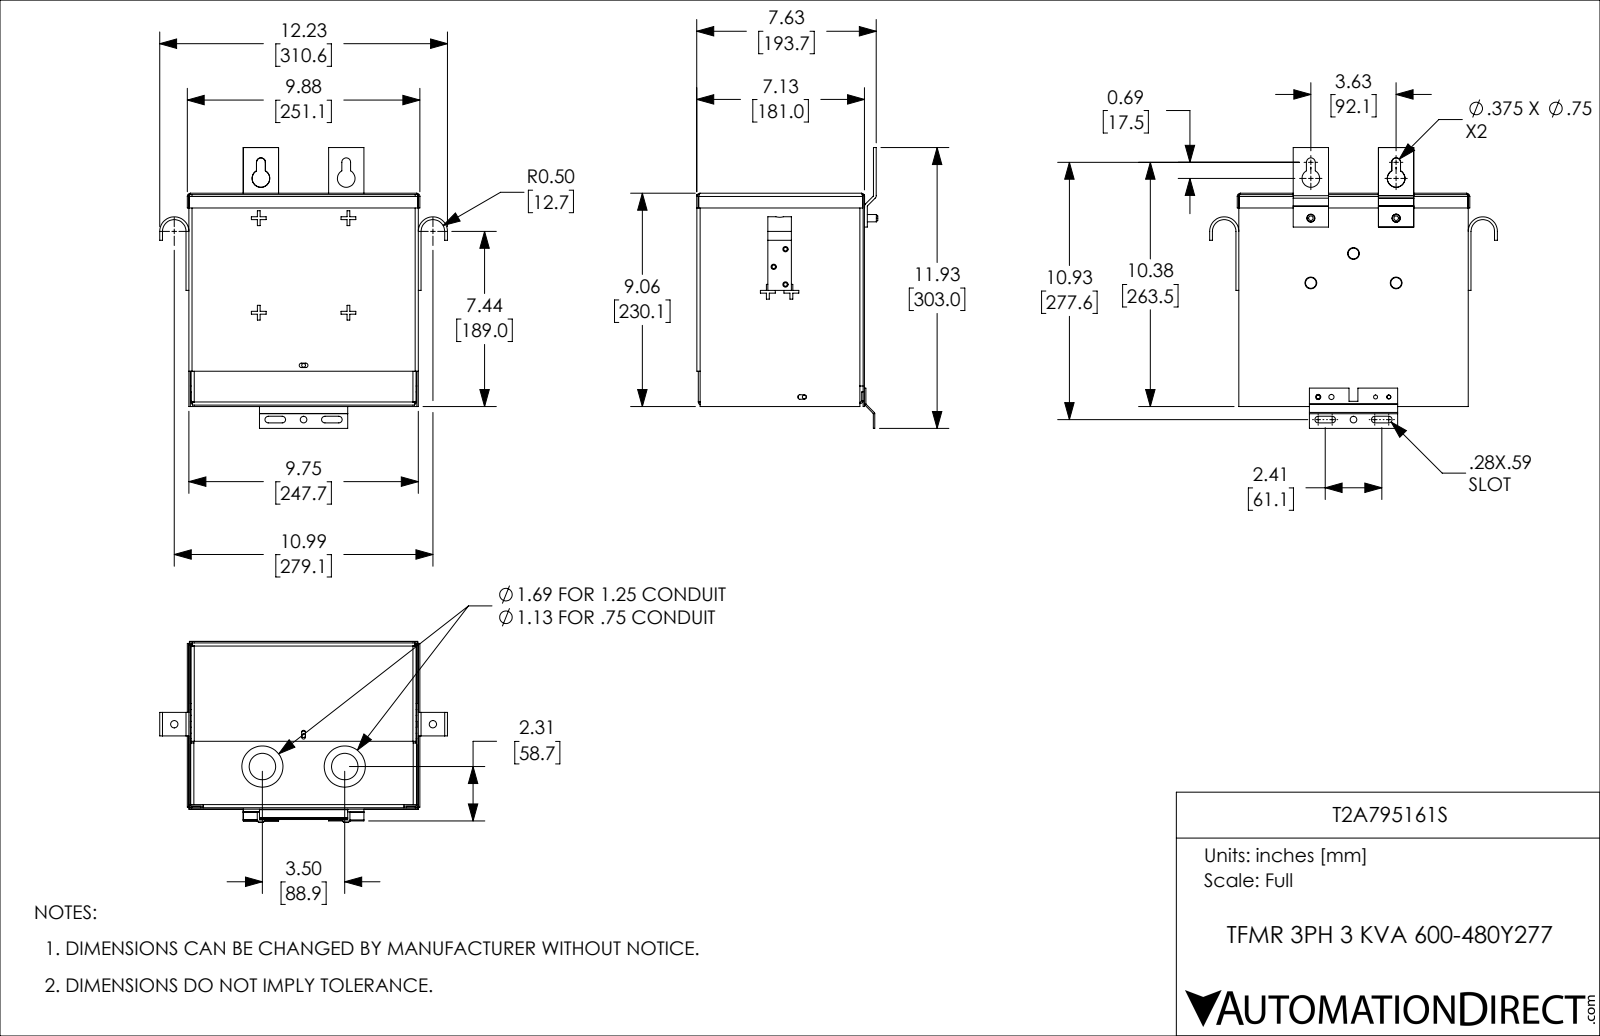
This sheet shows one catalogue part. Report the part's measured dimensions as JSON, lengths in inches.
{"part_name": "T2A795161S", "step_written_by": "SolidWorks 2017 (AUTOMOTIVE_DESIGN)", "units": "inches", "bodies": {"solids": 9, "faces": 621, "planar": 405, "cylindrical": 144, "other": 72}, "overall_size": [12.23, 11.929, 7.693], "volume_in3": 31.98, "surface_area_in2": 1026, "round_holes": [[0.16, 5], [0.172, 2], [0.219, 2], [0.281, 2], [0.313, 2], [0.344, 2], [0.75, 2], [1.125, 2], [1.75, 2], [0.173, 1], [0.187, 1]], "round_bosses_or_shafts": [[1.87, 2], [1.245, 2], [0.312, 2]], "partial_cylinders_radius": [[0.075, 16], [0.135, 16], [0.094, 8], [0.141, 4], [0.02, 2], [0.03, 2], [0.078, 2], [0.08, 2]], "face_to_face_distances": [0.06, 7.062, 0.059, 7.002, 8.94, 7.122, 9.69, 9.691, 9.75, 9.631], "hole_center_spacings": [0.563, 1.342, 1.638, 1.687, 1.781, 2.014, 2.187, 2.437]}
